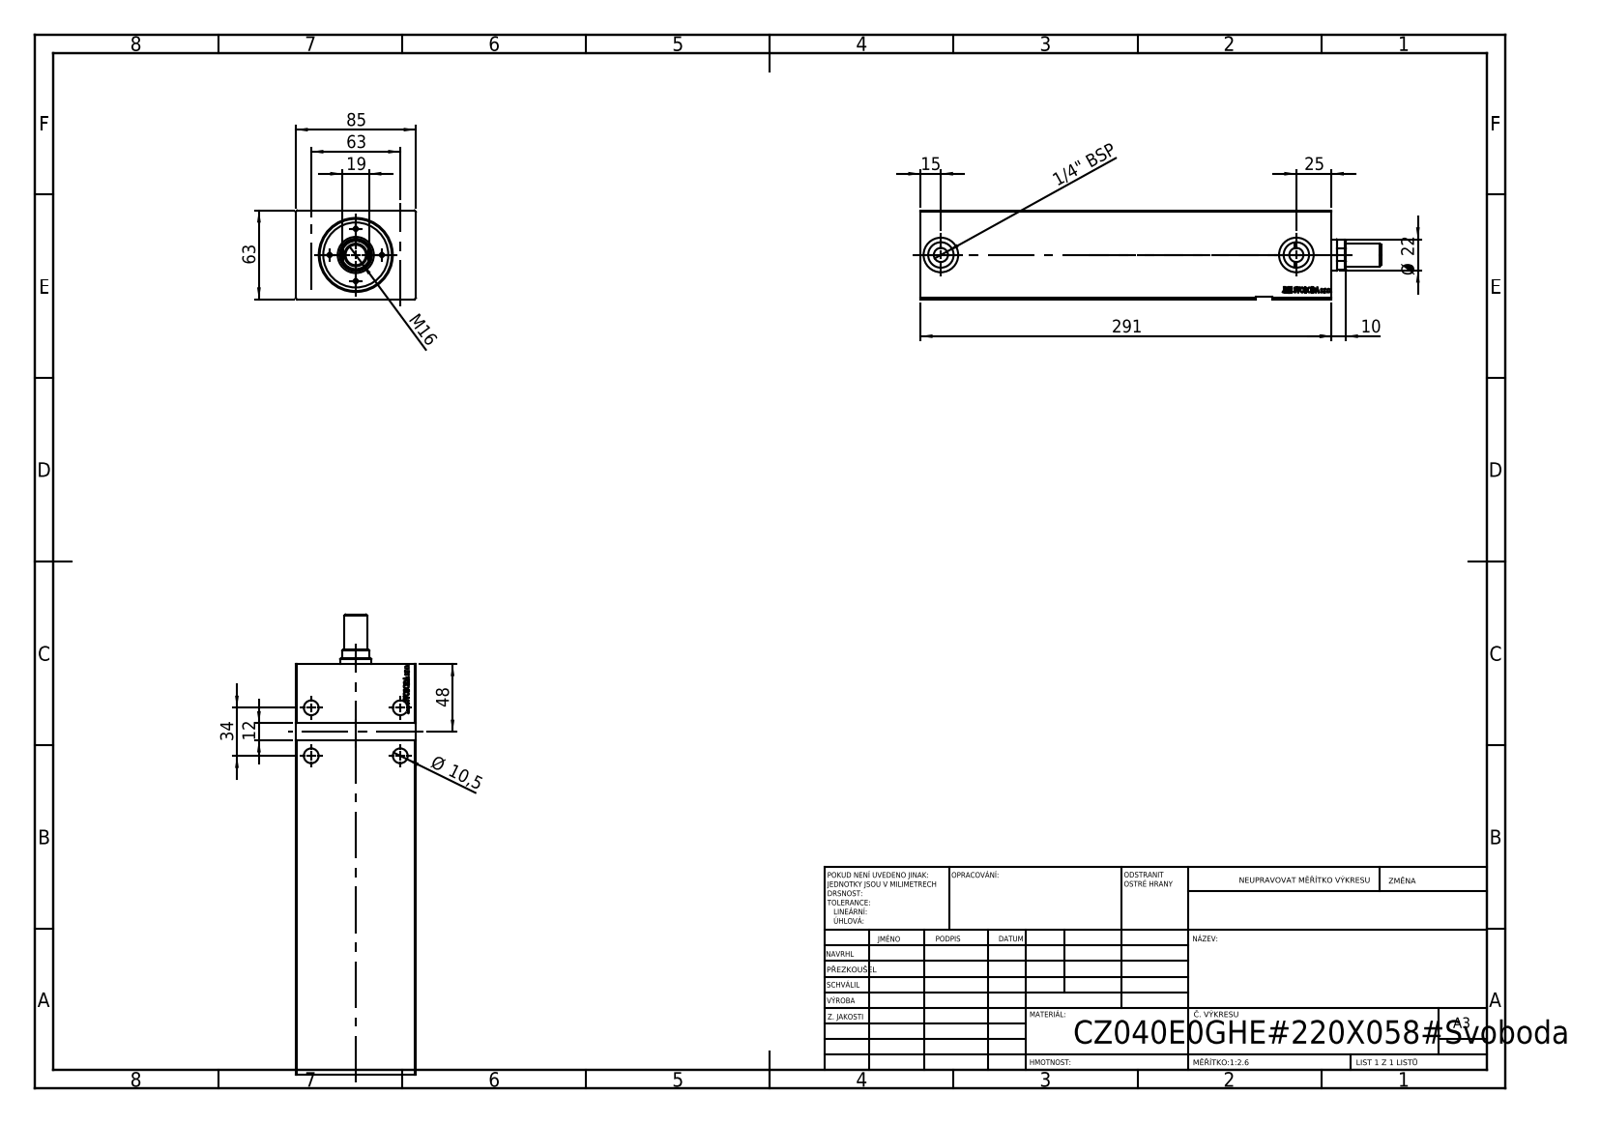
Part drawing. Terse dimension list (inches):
written by: SolidWorks 2019 (CONFIG_CONTROL_DESIGN)
unit: in
bodies: 1 solid, 797 faces (383 planar, 30 cylindrical, 384 other)
size: 11.457 × 3.346 × 2.48
volume: 71.52 in³; area: 218.1 in²
holes: 4× ⌀0.413, 2× ⌀0.315, 2× ⌀0.394, 2× ⌀0.709, 2× ⌀0.965, 1× ⌀1.417, 1× ⌀1.575, 1× ⌀2.008
face distances: 2.48, 3.346, 11.457, 10.854, 0.602, 0.079, 2.402, 11.449, 0.594, 4.064
hole spacings: 1.339, 2.48, 2.819, 0.707, 1.367, 1.798, 2.146, 7.963
